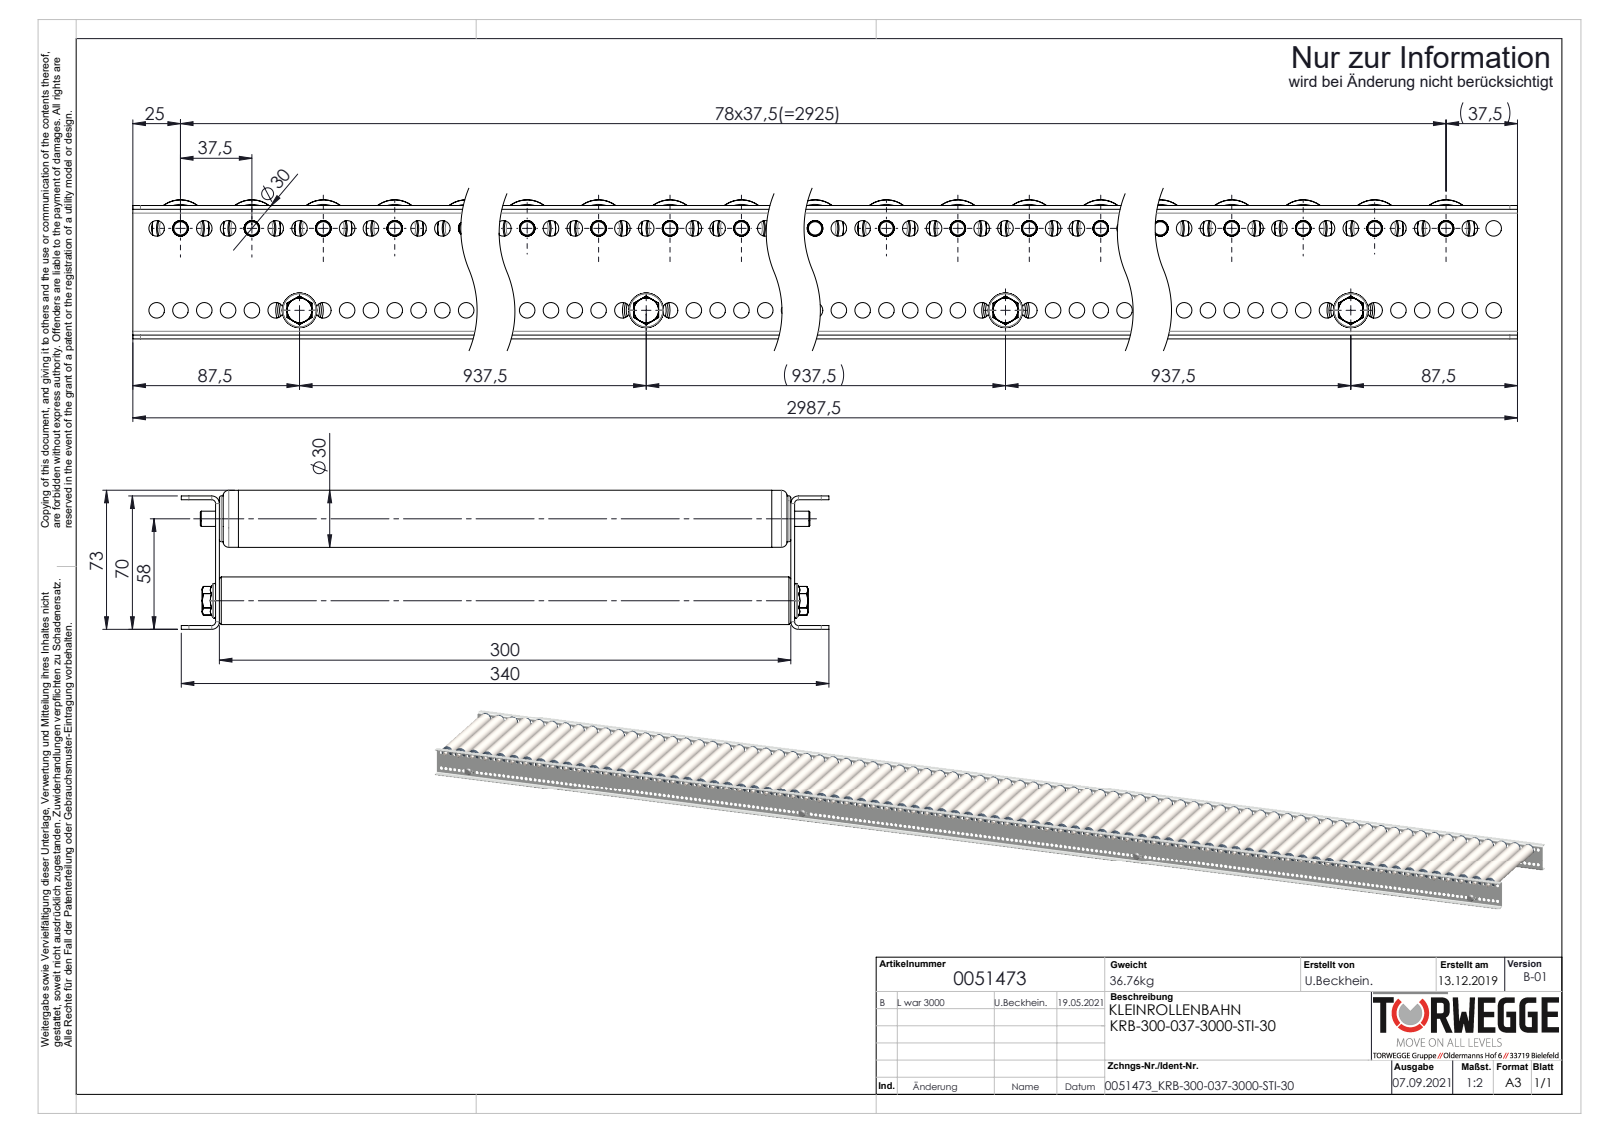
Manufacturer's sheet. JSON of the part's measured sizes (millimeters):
{"part_name": "S100994_Sperrzahnschraube_M08x16-8.8-A2K; 0040250_DRUCK-FEDER-8mm; Traversen_KFG_L300; 0042503_Typ-KUT50-30x1,5-A8 (+6 more)", "step_written_by": "SolidWorks 2020 (AUTOMOTIVE_DESIGN)", "units": "millimeters", "bodies": {"solids": 496, "faces": 20898, "planar": 6524, "cylindrical": 8320, "other": 6054}, "overall_size": [2987.5, 340, 73], "volume_mm3": 5655000, "surface_area_mm2": 7145000, "round_holes": [[8.2, 476], [8, 79], [8.1, 79], [23.2, 79], [25.2, 79], [27, 79], [6.8, 4], [21, 4]], "round_bosses_or_shafts": [[30, 79], [29.9, 79], [27.1, 79], [26.8, 79], [24, 79], [14, 79], [25, 4], [8, 4]], "partial_cylinders_radius": [[5.05, 79], [4, 8], [2, 4]], "face_to_face_distances": [2, 302, 300, 68, 304, 70, 66, 10, 290, 20], "hole_center_spacings": [12.5, 25, 37.5, 50, 62.5, 75, 87.5, 100]}
